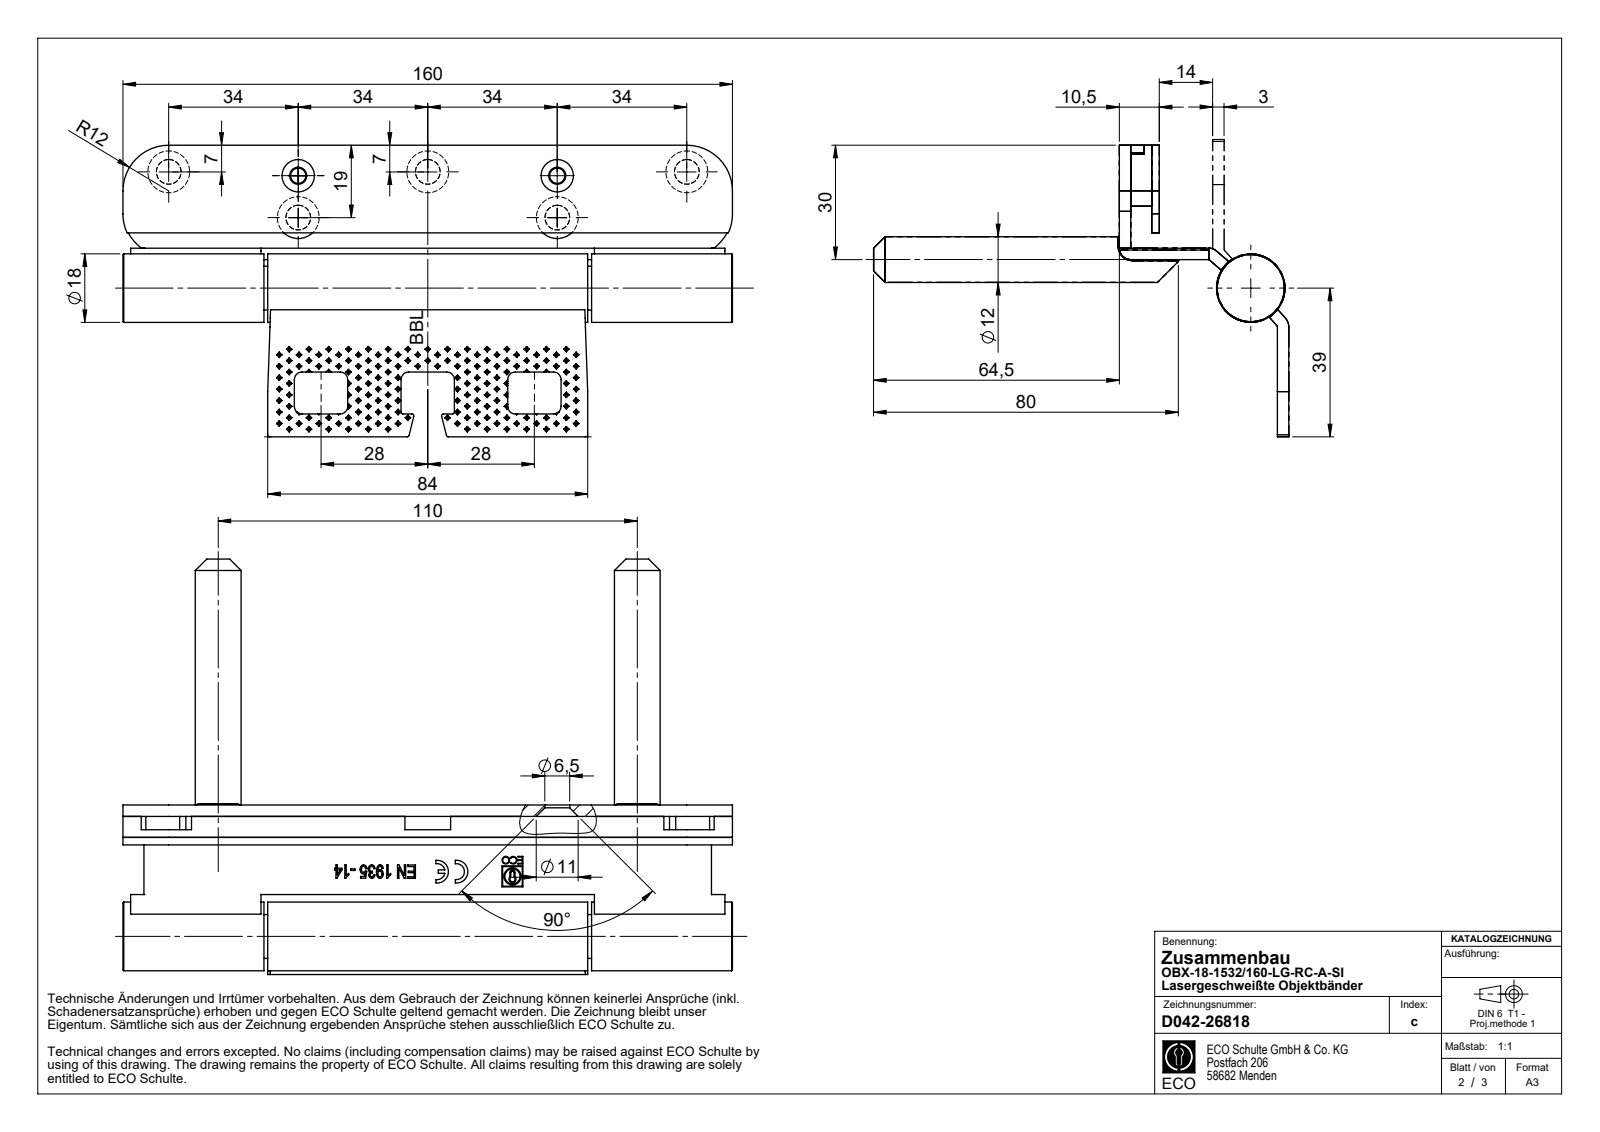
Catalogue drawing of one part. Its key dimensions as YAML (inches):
part_name: "D043-19098; B03164; D042-26479; D044-14309 (+8 more)"
step_written_by: "SolidWorks 2020 (CONFIG_CONTROL_DESIGN)"
units: inches
bodies: {solids: 17, faces: 2042, planar: 1738, cylindrical: 181, other: 123}
overall_size: [6.299, 4.252, 1.89]
volume: 6.074
surface_area: 96.23
round_holes:
  - {diameter: 0.256, count: 5}
  - {diameter: 0.079, count: 2}
  - {diameter: 0.157, count: 2}
  - {diameter: 0.197, count: 2}
  - {diameter: 0.02, count: 1}
  - {diameter: 0.177, count: 1}
  - {diameter: 0.311, count: 1}
round_bosses_or_shafts:
  - {diameter: 0.472, count: 3}
  - {diameter: 0.276, count: 2}
  - {diameter: 0.709, count: 1}
  - {diameter: 0.465, count: 1}
  - {diameter: 0.453, count: 1}
  - {diameter: 0.303, count: 1}
  - {diameter: 0.157, count: 1}
  - {diameter: 0.065, count: 1}
partial_cylinders:
  - {radius: 0.079, count: 10}
  - {radius: 0.02, count: 9}
  - {radius: 0.01, count: 6}
  - {radius: 0.138, count: 6}
  - {radius: 0.472, count: 6}
  - {radius: 0.004, count: 4}
  - {radius: 0.098, count: 4}
  - {radius: 0.027, count: 2}
face_to_face_distances: [0.118, 0.079, 0.217, 0.335, 0.295, 0.965, 0.413, 0.551, 0.63, 0.157]
hole_center_spacings: [1.339, 1.42, 2.677, 0.433, 2.712, 4.016, 4.043, 0.077]
